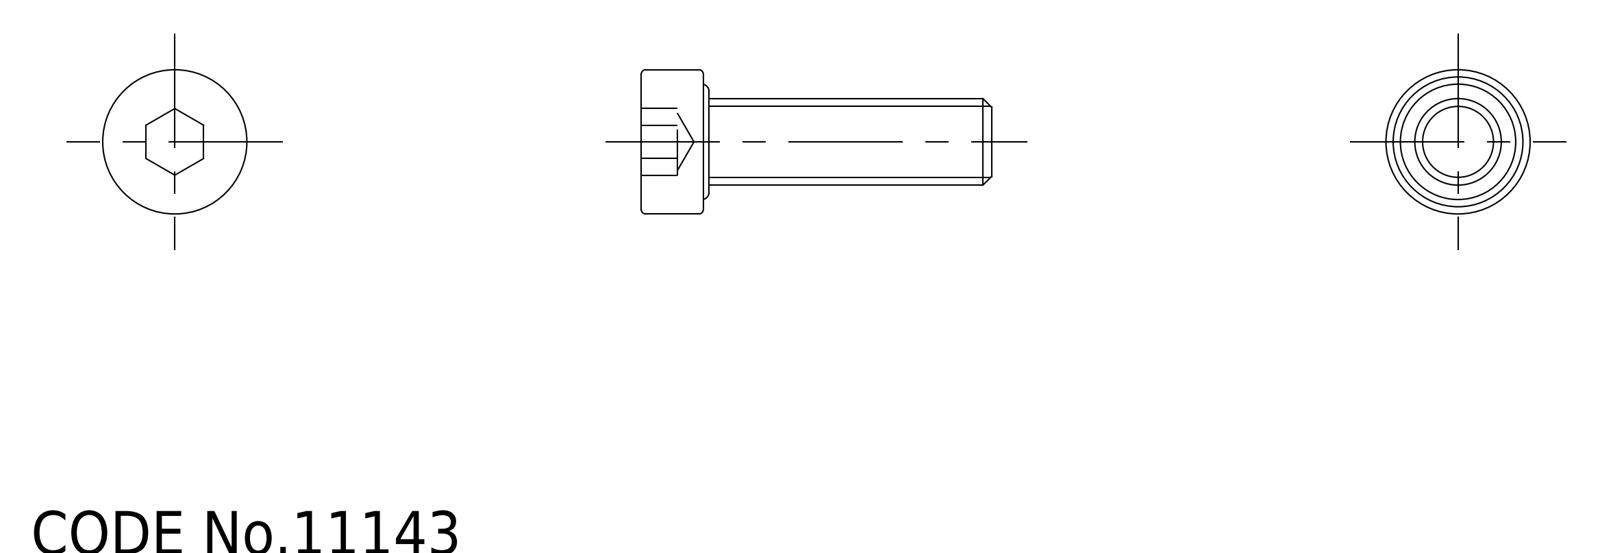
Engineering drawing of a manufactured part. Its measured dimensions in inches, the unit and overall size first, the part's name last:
Units: inches
Overall size (bounding box): 0.957 × 0.394 × 0.394
Round holes (diameter × count): ⌀0.354 ×1
Round bosses / shafts (diameter × count): ⌀0.394 ×1, ⌀0.236 ×1
Main face-to-face distances: 0.146, 0.957, 0.811, 0.157, 0.098, 0.047, 0.858, 0.169, 0.071, 0.024
Volume: 0.052 in³ · Surface area: 1.22 in²
Bodies: 2 solids, 27 faces (11 planar, 6 cylindrical, 10 other)
Part name (STEP PRODUCT): screw; TL_418_M6_20
STEP written by: SolidWorks 2015 (AUTOMOTIVE_DESIGN)
